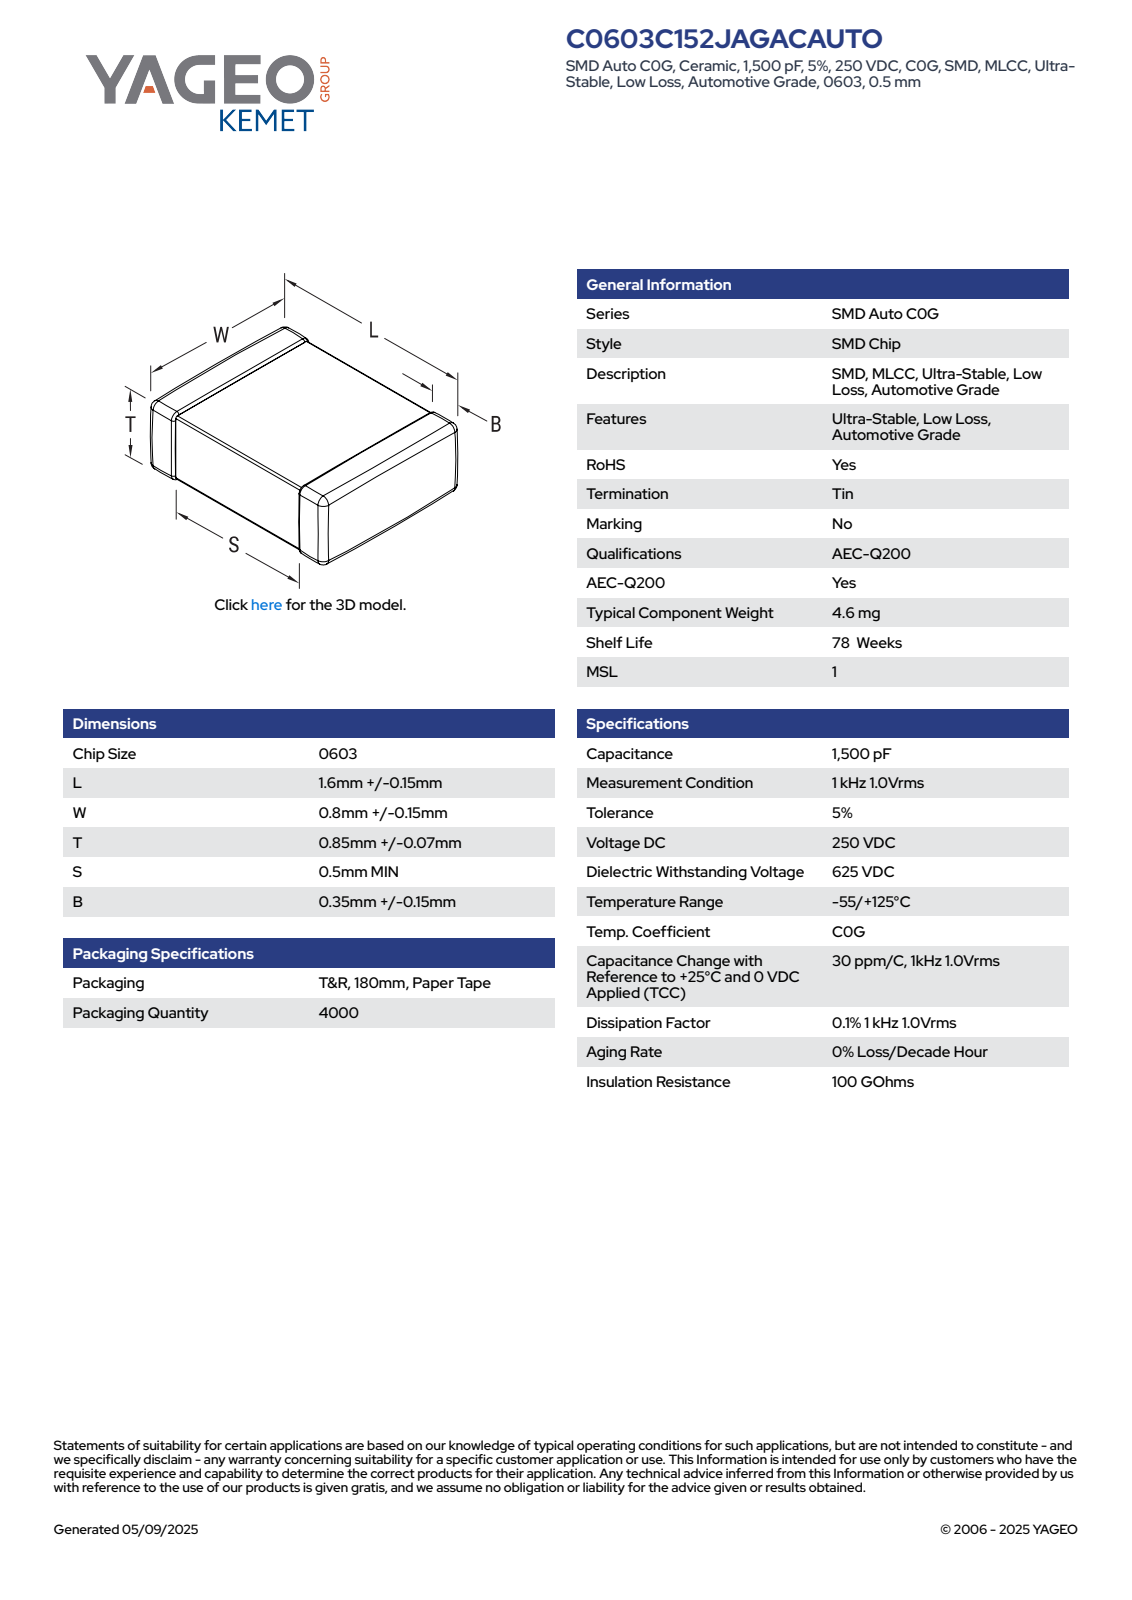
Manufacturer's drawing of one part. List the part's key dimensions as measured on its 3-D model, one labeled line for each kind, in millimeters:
Part name (STEP PRODUCT): CCS_CCSTD_0603_L1.75W0.95T0.92B0.35
STEP written by: SolidWorks 2014 (AUTOMOTIVE_DESIGN)
Units: millimetres
Bodies: 4 solids, 121 faces (71 planar, 34 cylindrical, 16 other)
Overall size (bounding box): 1.75 × 0.95 × 0.92
Volume: 1 mm³ · Surface area: 8 mm²
Main face-to-face distances: 0.9, 0.93, 0.91, 0.88, 1.75, 0.92, 0.95, 0.89, 0.81, 0.94
